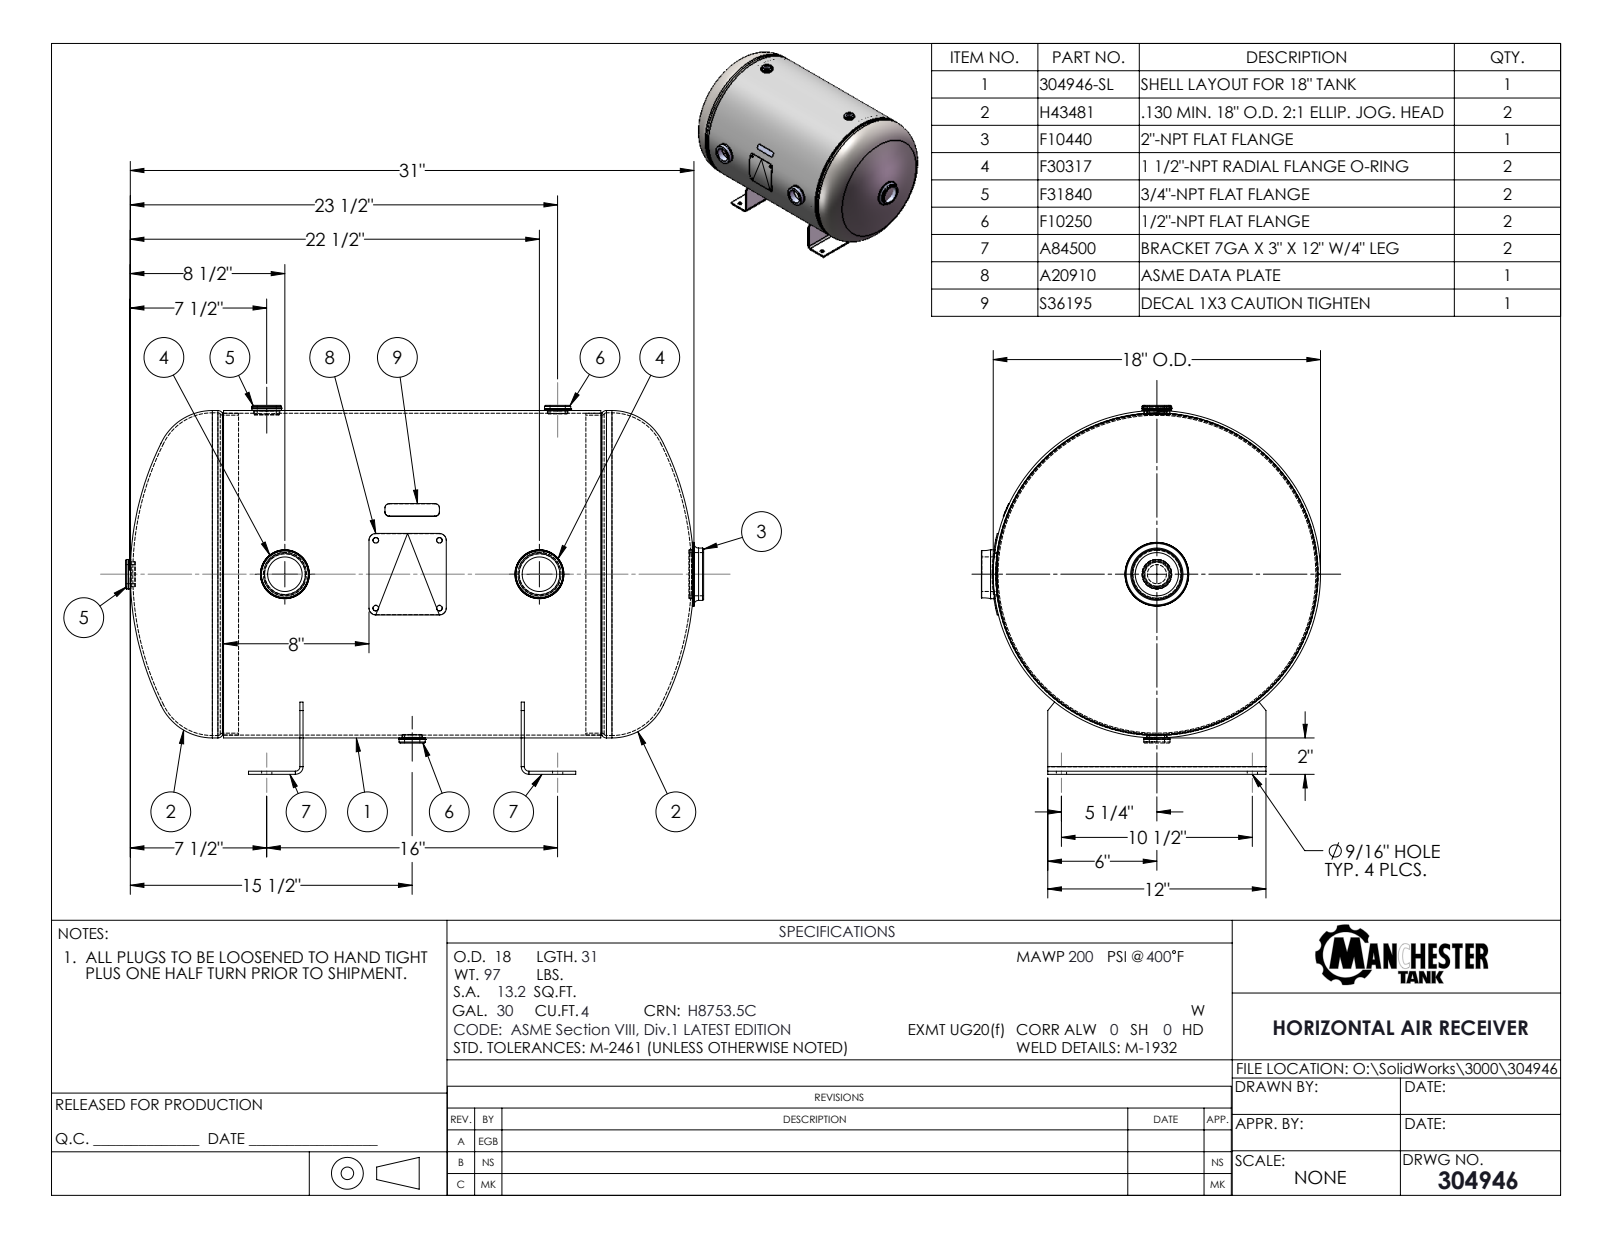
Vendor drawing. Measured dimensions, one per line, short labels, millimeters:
name: 304946
written by: SolidWorks 2014 (AUTOMOTIVE_DESIGN)
unit: mm
bodies: 0 solids, 198 faces (47 planar, 67 cylindrical, 84 other)
size: 807.55 × 515.14 × 473.69
holes: 4× ⌀14.29, 2× ⌀21.34, 2× ⌀26.67, 2× ⌀48.26, 1× ⌀60.33, 1× ⌀449.38
bosses: 2× ⌀68.28, 2× ⌀41.27, 2× ⌀36.83, 2× ⌀36.53, 1× ⌀457.2, 1× ⌀449.33, 1× ⌀88.9, 1× ⌀73.03
rounds: 6× R6.35, 2× R10.72, 1× R230.12
face distances: 4.37, 309.17, 304.8, 313.54, 106.76, 111.13, 415.93, 420.3, 527.06, 34.93
hole spacings: 133.35, 243.05, 427.72, 406.4, 203.2, 266.7, 486.1, 355.6
